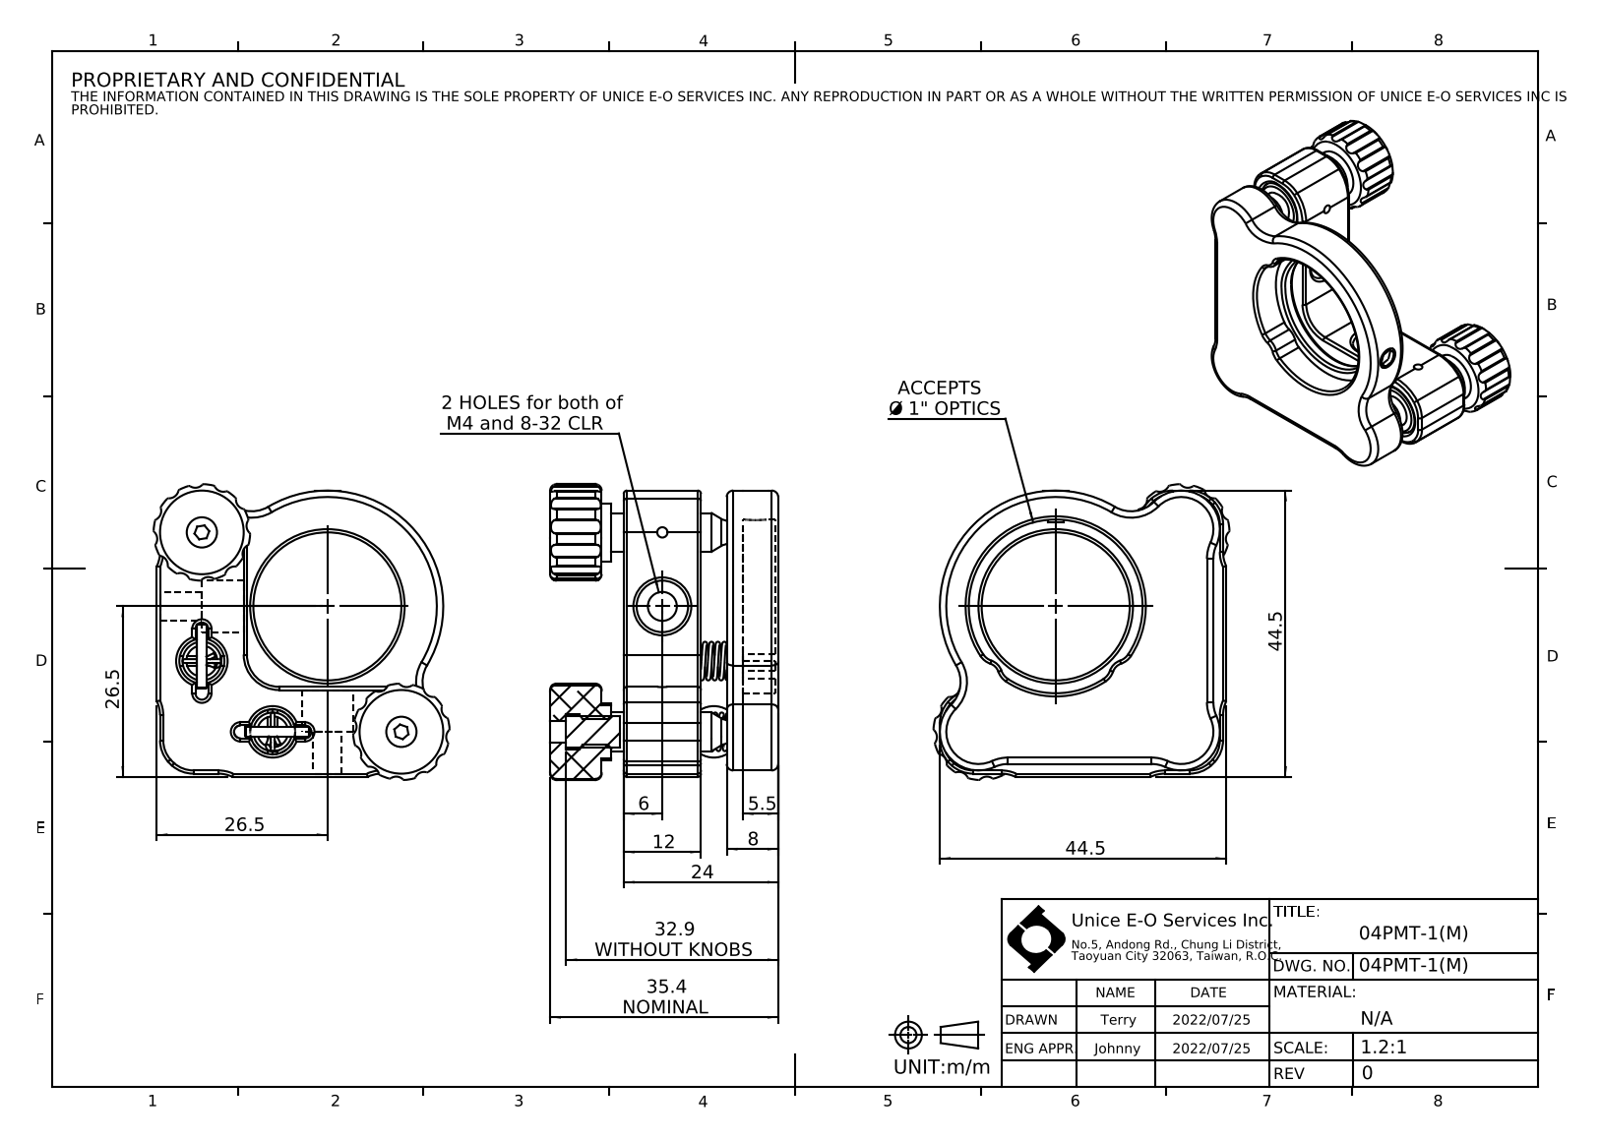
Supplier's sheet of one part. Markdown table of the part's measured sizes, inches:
| quantity | value |
| --- | --- |
| part name | 04PMT-1(M) |
| STEP written by | SolidWorks 2021 (CONFIG_CONTROL_DESIGN) |
| units | inches |
| bodies | 21 solids, 612 faces (111 planar, 304 cylindrical, 197 other) |
| overall size | 1.81 × 1.81 × 1.395 |
| volume | 1.351 in³ |
| surface area | 24.41 in² |
| round holes (diameter × count) | 0.039 × 4, 0.063 × 2, 0.067 × 2, 0.157 × 2, 0.177 × 2, 0.185 × 2, 0.204 × 2, 0.236 × 2, 0.248 × 2, 0.276 × 2, 0.315 × 2, 0.374 × 2 |
| round bosses / shafts (diameter × count) | 0.059 × 6, 0.024 × 6, 0.354 × 2, 0.157 × 1, 0.098 × 1 |
| partial cylindrical surfaces (radius × count) | 0.012 × 48, 0.059 × 25, 0.02 × 20, 0.197 × 19, 0.039 × 8, 0.098 × 6, 0.03 × 4, 0.236 × 3 |
| main face-to-face distances | 0.472, 0.315, 0.157, 0.63, 0.945, 1.08, 0.059, 0.276, 0.079, 0.551 |
| hole center spacings | 0.453, 0.679, 0.787, 0.837, 0.891, 0.984, 1.295, 0.335 |
